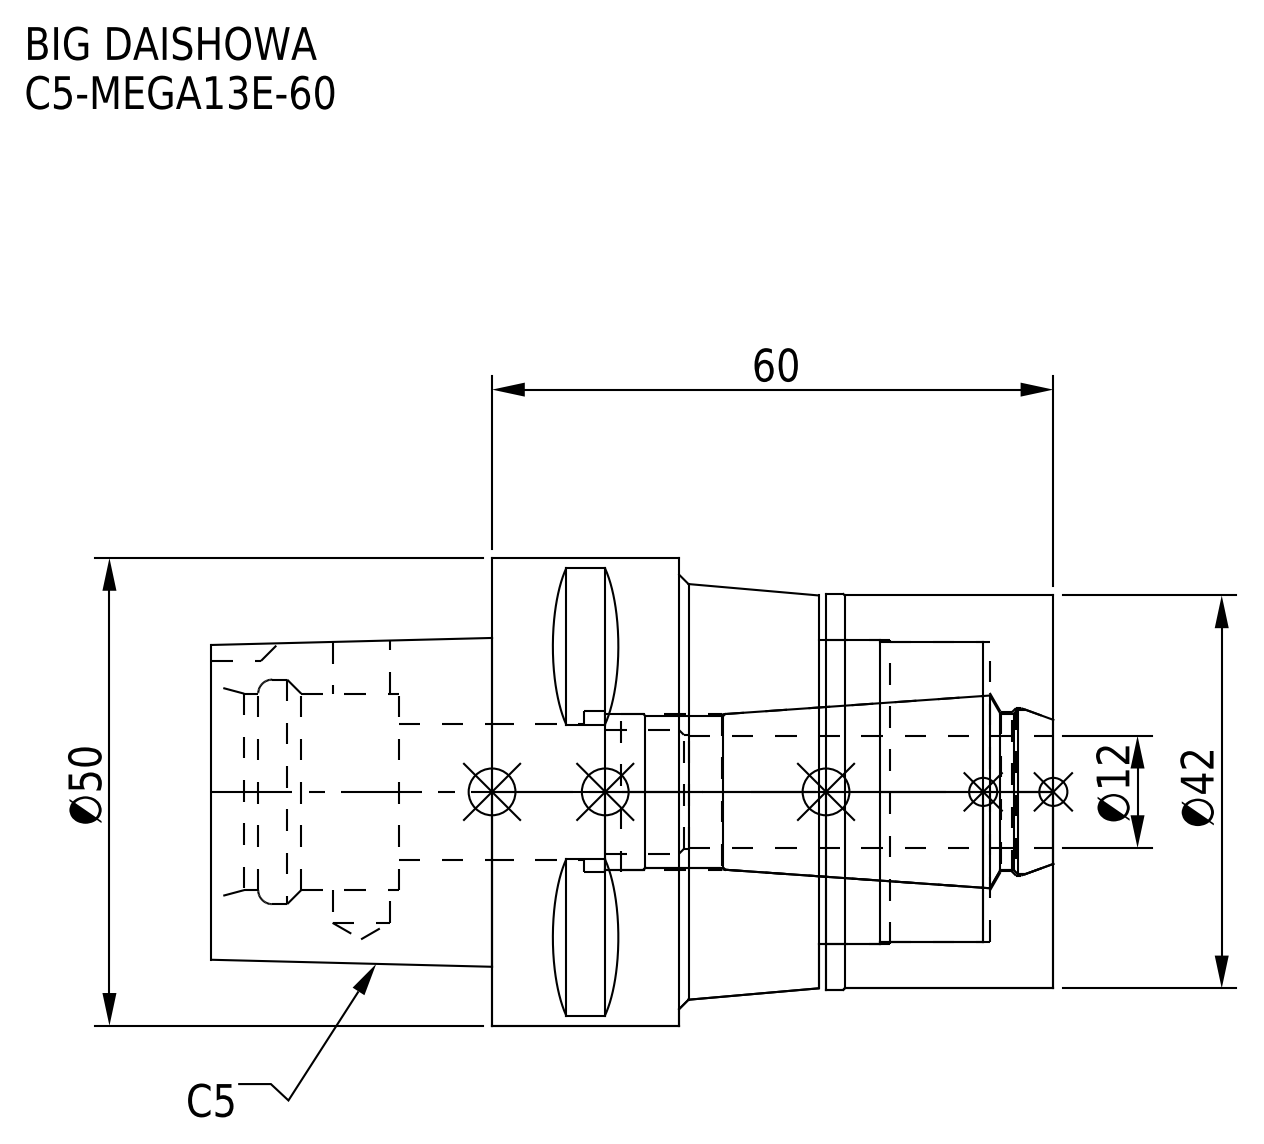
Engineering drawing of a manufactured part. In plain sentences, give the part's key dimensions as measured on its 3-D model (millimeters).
The part is named "DXF_TEMP_ASSY_ASM_4_ASM.stp; C5-MEGA13E-60-120_ASM.stp; C5-MEGA13E-60_1.stp; C5-MEGA13E-60 (+3 more)". Its 3-D file was written by "SolidWorks 2019 (CONFIG_CONTROL_DESIGN)". It is 2 solids with 94 faces: 35 planar, 35 cylindrical and 24 other. Overall it measures 90 by 50 by 50 millimeters. Its volume is 98 207 cubic millimeters and its surface area 26 140 square millimeters. Round holes: 1 of diameter 6.1, 1 of diameter 14.5, 1 of diameter 16.6, 1 of diameter 17, 1 of diameter 17.2, 1 of diameter 17.9, 1 of diameter 21, 1 of diameter 24, 1 of diameter 32, 1 of diameter 32.5. Round bosses or shafts: 1 of diameter 50, 1 of diameter 42.3, 1 of diameter 42. Partial cylindrical surfaces (rounded edges, fillets, slot ends): 1 of radius 4. The main face-to-face distances are 60, 25.1, 24.3, 35.7, 30, 0.8, 34.9, 52.5, 6.8, 17.5.
